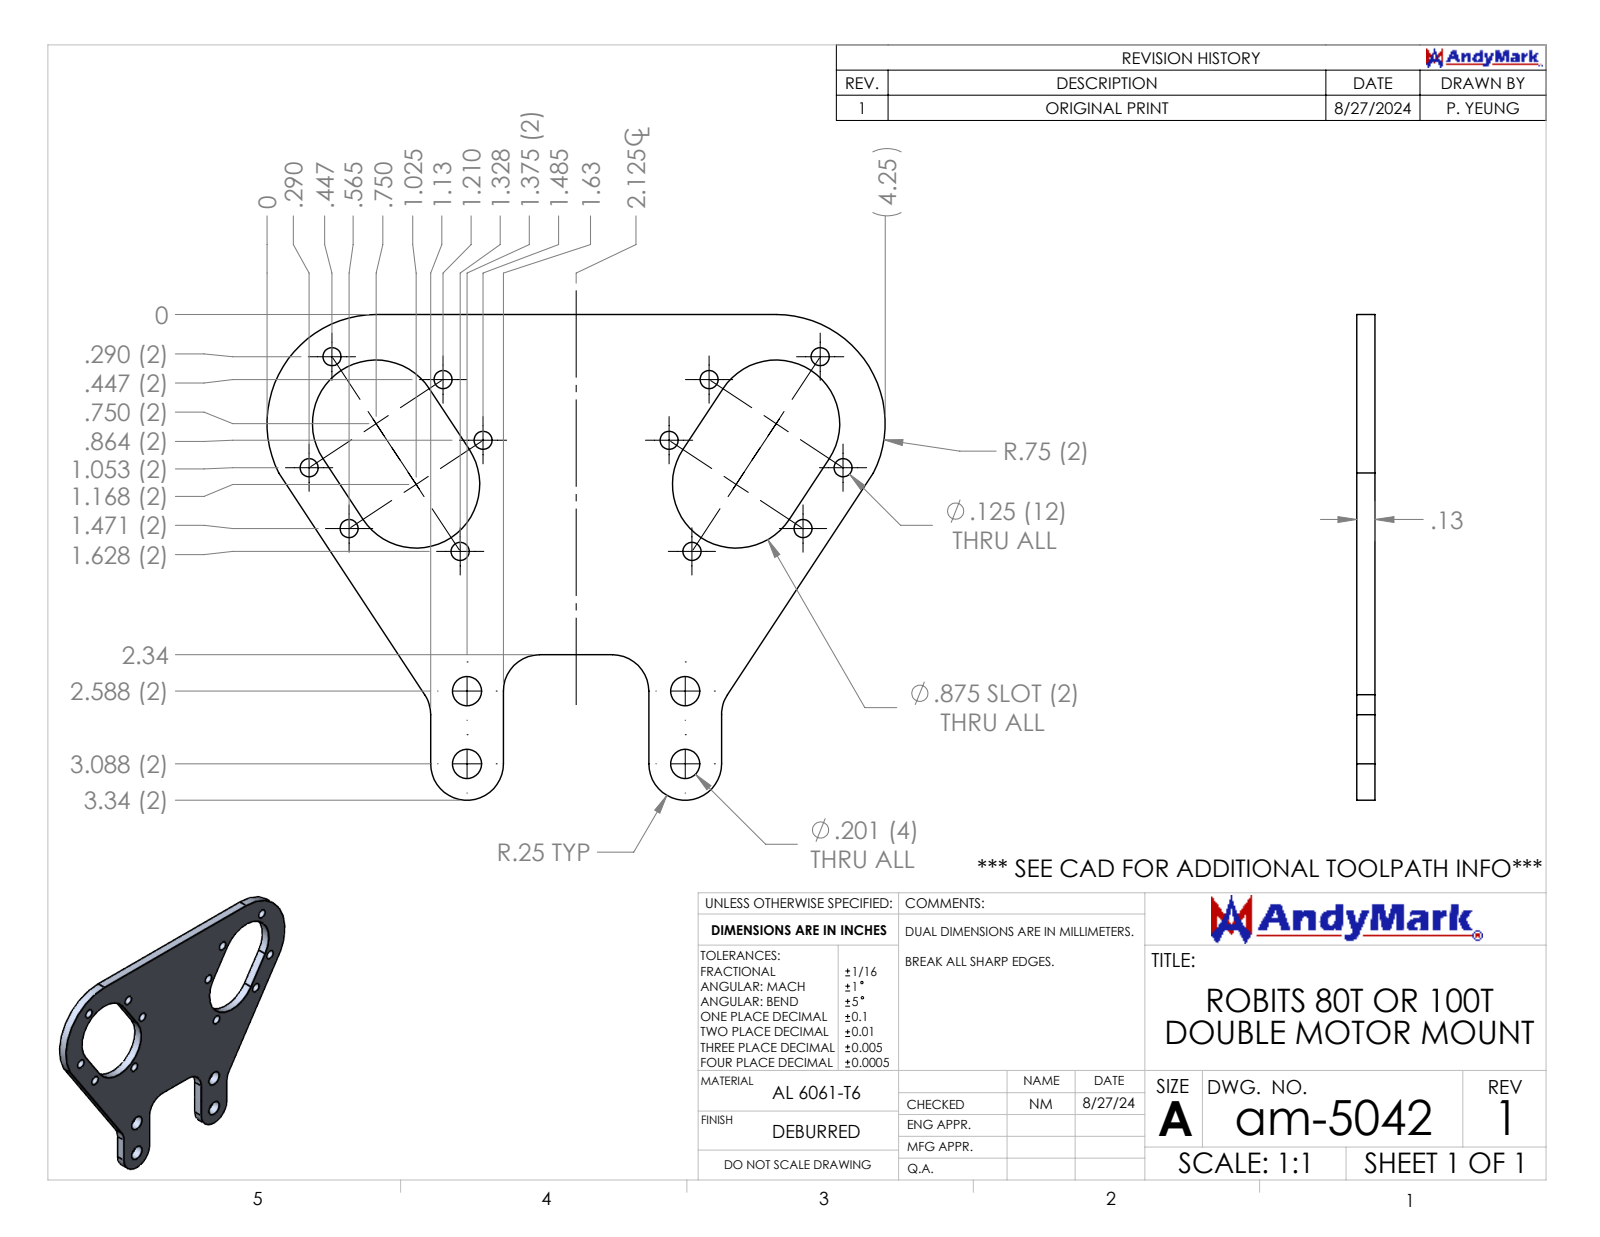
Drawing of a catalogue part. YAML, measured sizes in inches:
part_name: "am-5042 Robits 80T or 100T Double Motor Mount"
step_written_by: "SolidWorks 2024 (AUTOMOTIVE_DESIGN)"
units: inches
bodies: {solids: 1, faces: 61, planar: 14, cylindrical: 47, other: 0}
overall_size: [4.25, 3.338, 0.125]
volume: 0.893
surface_area: 17.92
round_holes:
  - {diameter: 0.125, count: 9}
  - {diameter: 0.201, count: 4}
  - {diameter: 0.125, count: 3}
partial_cylinders:
  - {radius: 0.25, count: 6}
  - {radius: 0.437, count: 3}
  - {radius: 0.75, count: 2}
  - {radius: 0.438, count: 1}
face_to_face_distances: [0.125, 1.182, 0.875, 0.307, 0.5, 1.5, 2.338, 1, 2]
hole_center_spacings: [1.187, 0.5, 0.78, 0.78, 1.102, 0.5, 0.961, 1.187]
